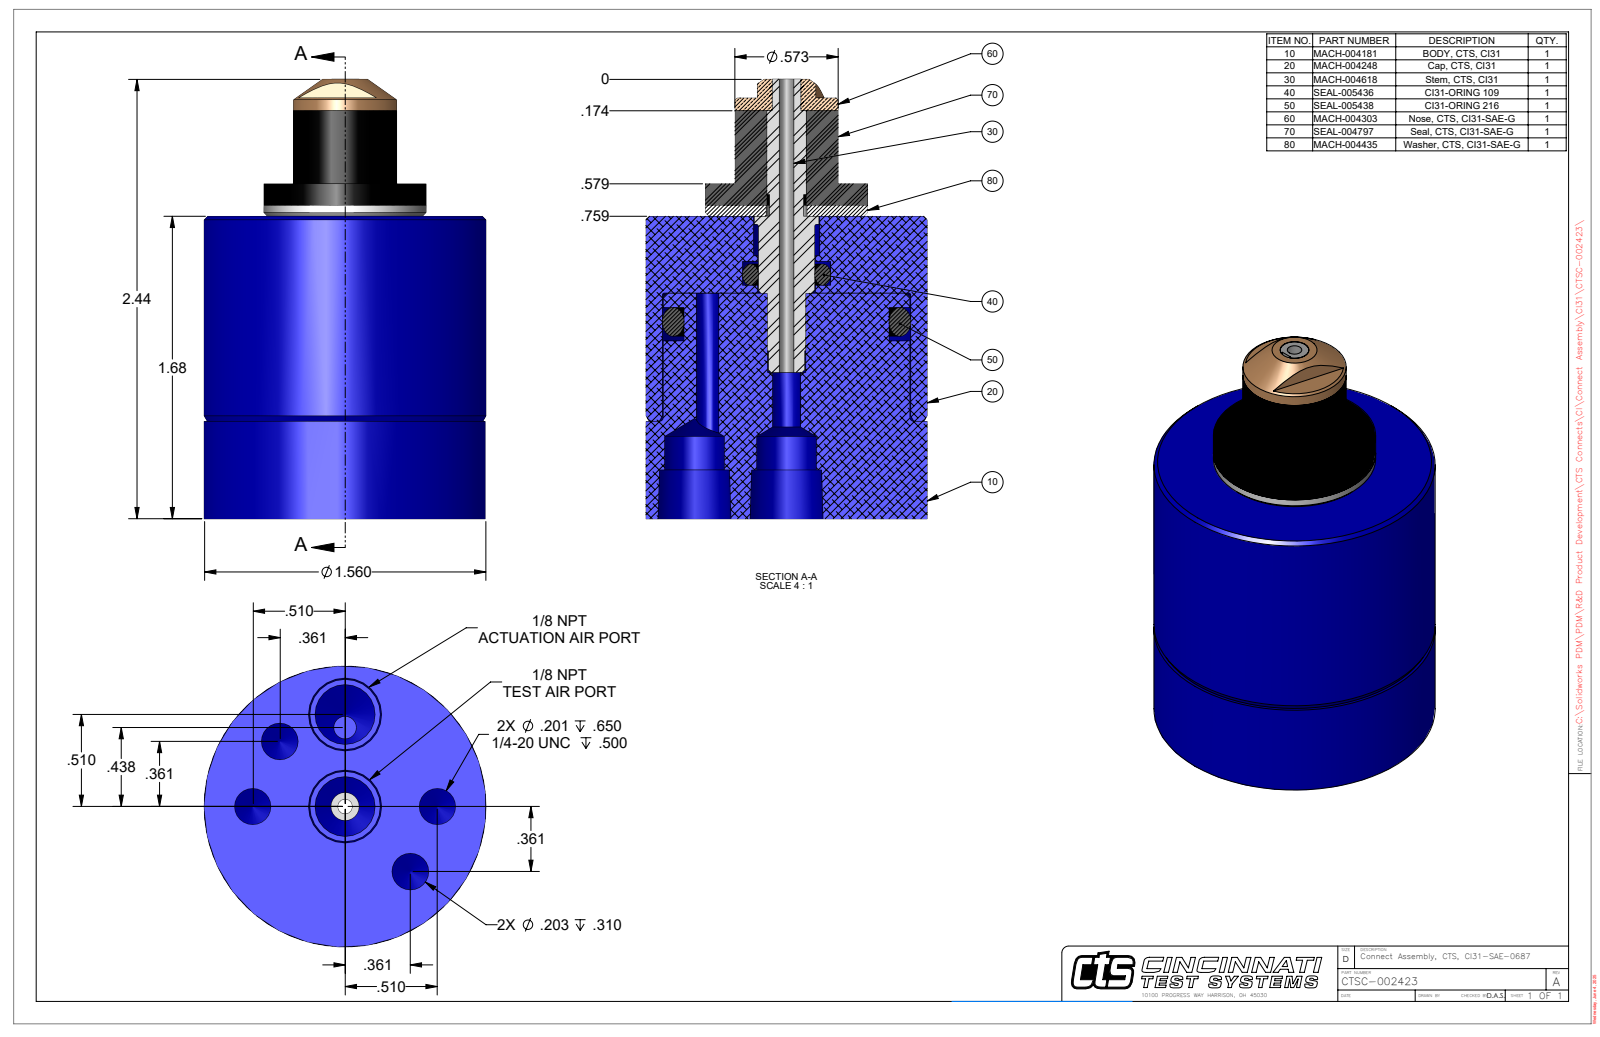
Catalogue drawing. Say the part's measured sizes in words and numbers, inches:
The part is named "CTSC-002423". Its 3-D file was written by "SolidWorks 2023 (AUTOMOTIVE_DESIGN)". It is 1 solid with 87 faces: 22 planar, 35 cylindrical and 30 other. Overall it measures 2.437 by 1.56 by 1.56 inches. Its volume is 3.256 cubic inches and its surface area 19.05 square inches. Round holes: 2 of diameter 0.201, 2 of diameter 0.203, 2 of diameter 0.332, 1 of diameter 0.081, 1 of diameter 0.125, 1 of diameter 0.156, 1 of diameter 0.368, 1 of diameter 1.377. Round bosses or shafts: 1 of diameter 1.56, 1 of diameter 1.365, 1 of diameter 0.9, 1 of diameter 0.573, 1 of diameter 0.357. Partial cylindrical surfaces (rounded edges, fillets, slot ends): 1 of radius 0.079. The main face-to-face distances are 1.677, 1.857, 0.18, 0.542, 1.135, 1.315, 2.332, 1.79, 0.655, 0.475. The hole center spacings are 0.51, 0.39, 0.942, 0.672, 0.721, 0.072, 0.369, 0.437.
